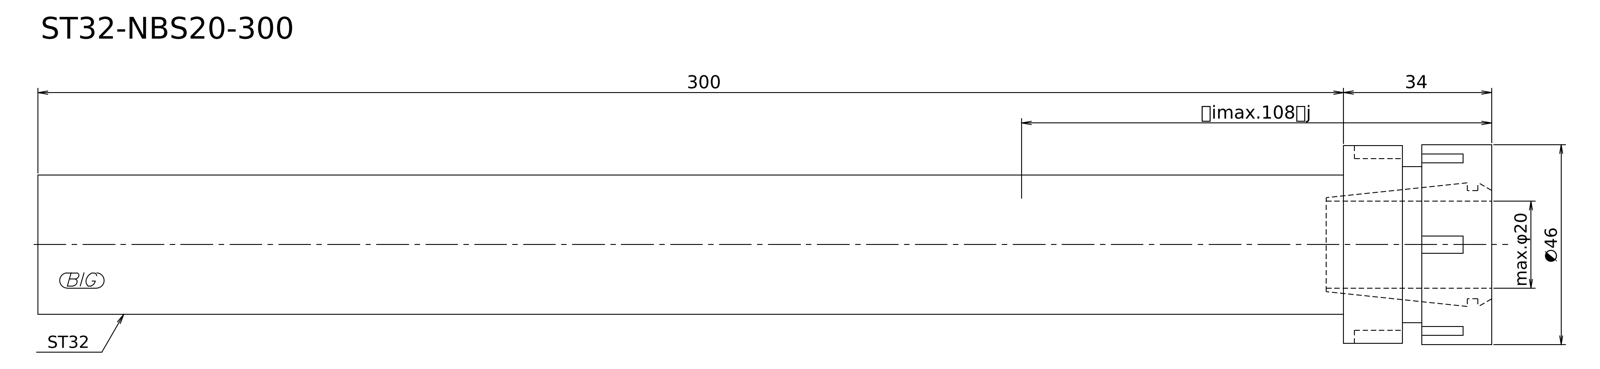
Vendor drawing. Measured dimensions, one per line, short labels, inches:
written by: Kubotek KeyCreator V8.5.1 (14335) (CONFIG_CONTROL_DESIGN)
unit: in
bodies: 1 solid, 9 faces (5 planar, 4 cylindrical, 0 other)
size: 13.15 × 1.811 × 1.811
volume: 17.97 in³; area: 61.15 in²
bosses: 1× ⌀1.811, 1× ⌀1.791, 1× ⌀1.417, 1× ⌀1.26
face distances: 1.339, 13.15, 11.811, 0.63, 0.709, 12.52, 0.807, 0.177, 0.531, 12.343
